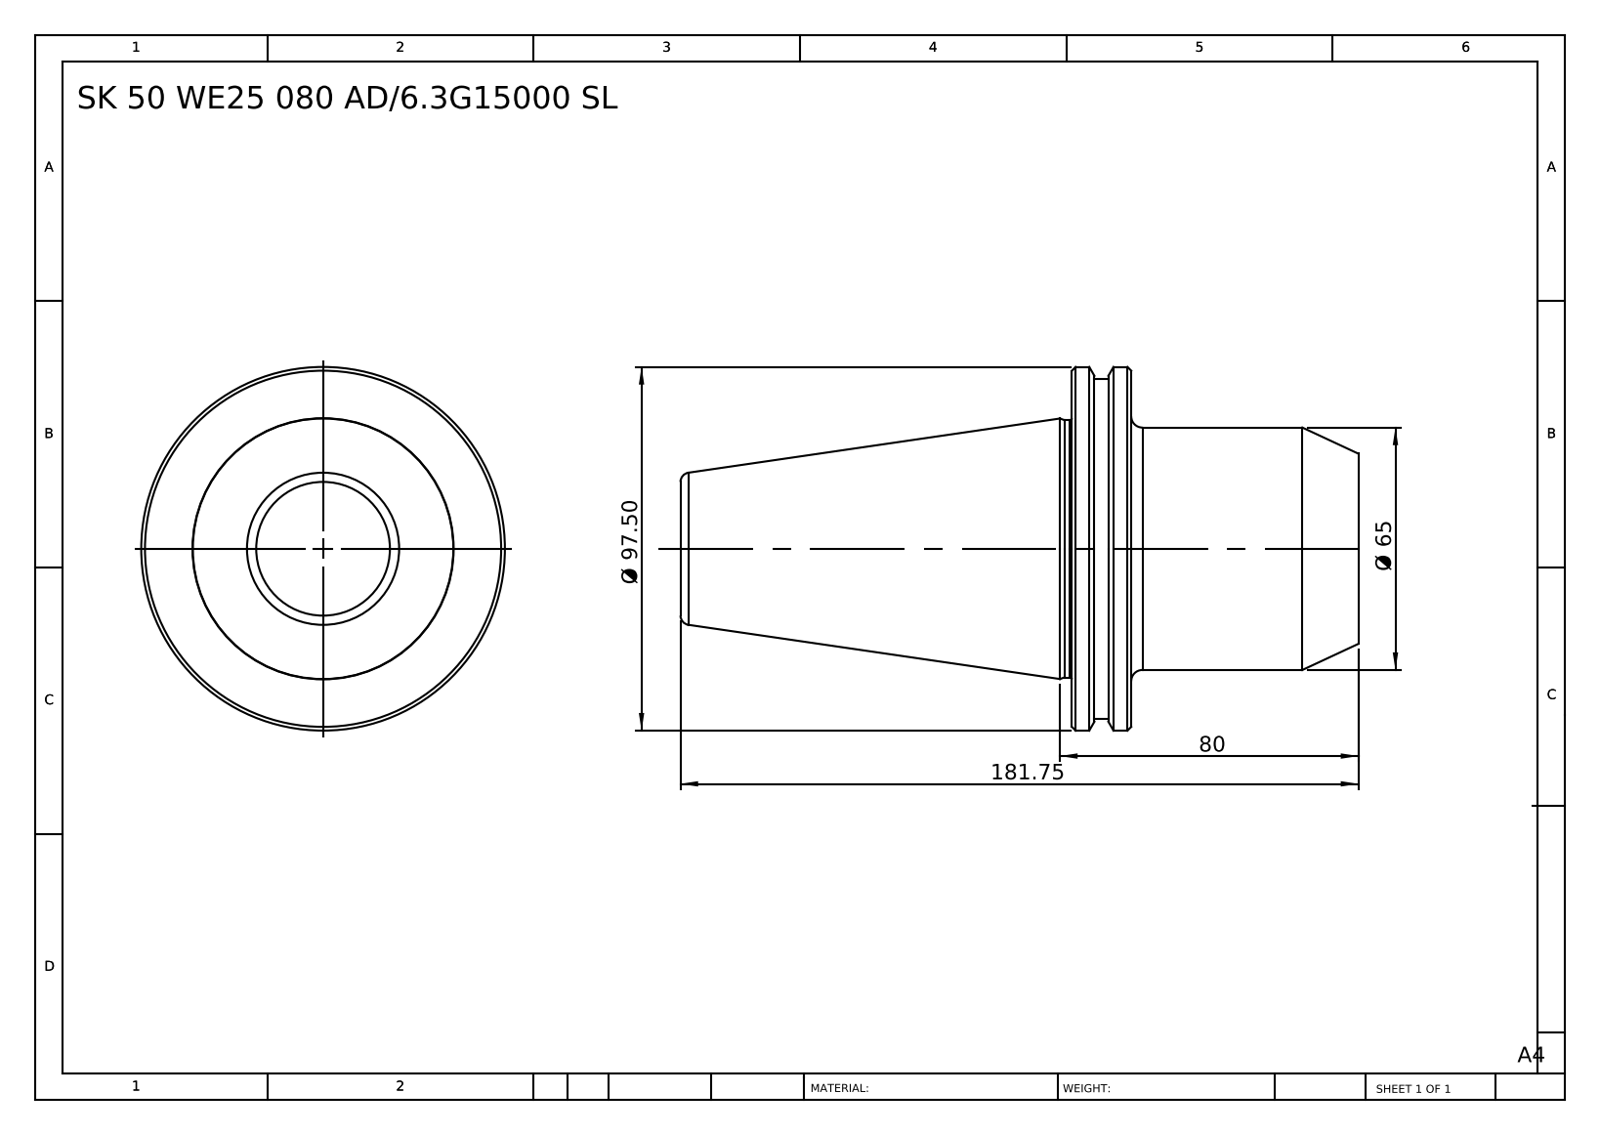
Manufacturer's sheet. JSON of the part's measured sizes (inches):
{"part_name": "SK50 WE25 080 AD-6.3G15000 SL", "step_written_by": "SolidWorks 2014 (CONFIG_CONTROL_DESIGN)", "units": "inches", "bodies": {"solids": 1, "faces": 36, "planar": 6, "cylindrical": 10, "other": 20}, "overall_size": [7.156, 3.839, 3.839], "volume_in3": 34.54, "surface_area_in2": 73.45, "round_bosses_or_shafts": [[3.839, 1], [3.583, 1], [2.717, 1], [2.559, 1]], "face_to_face_distances": [0.626, 2.398, 3.024, 7.156, 4.758, 4.132, 2.639, 0.241, 0.385, 4.517]}
